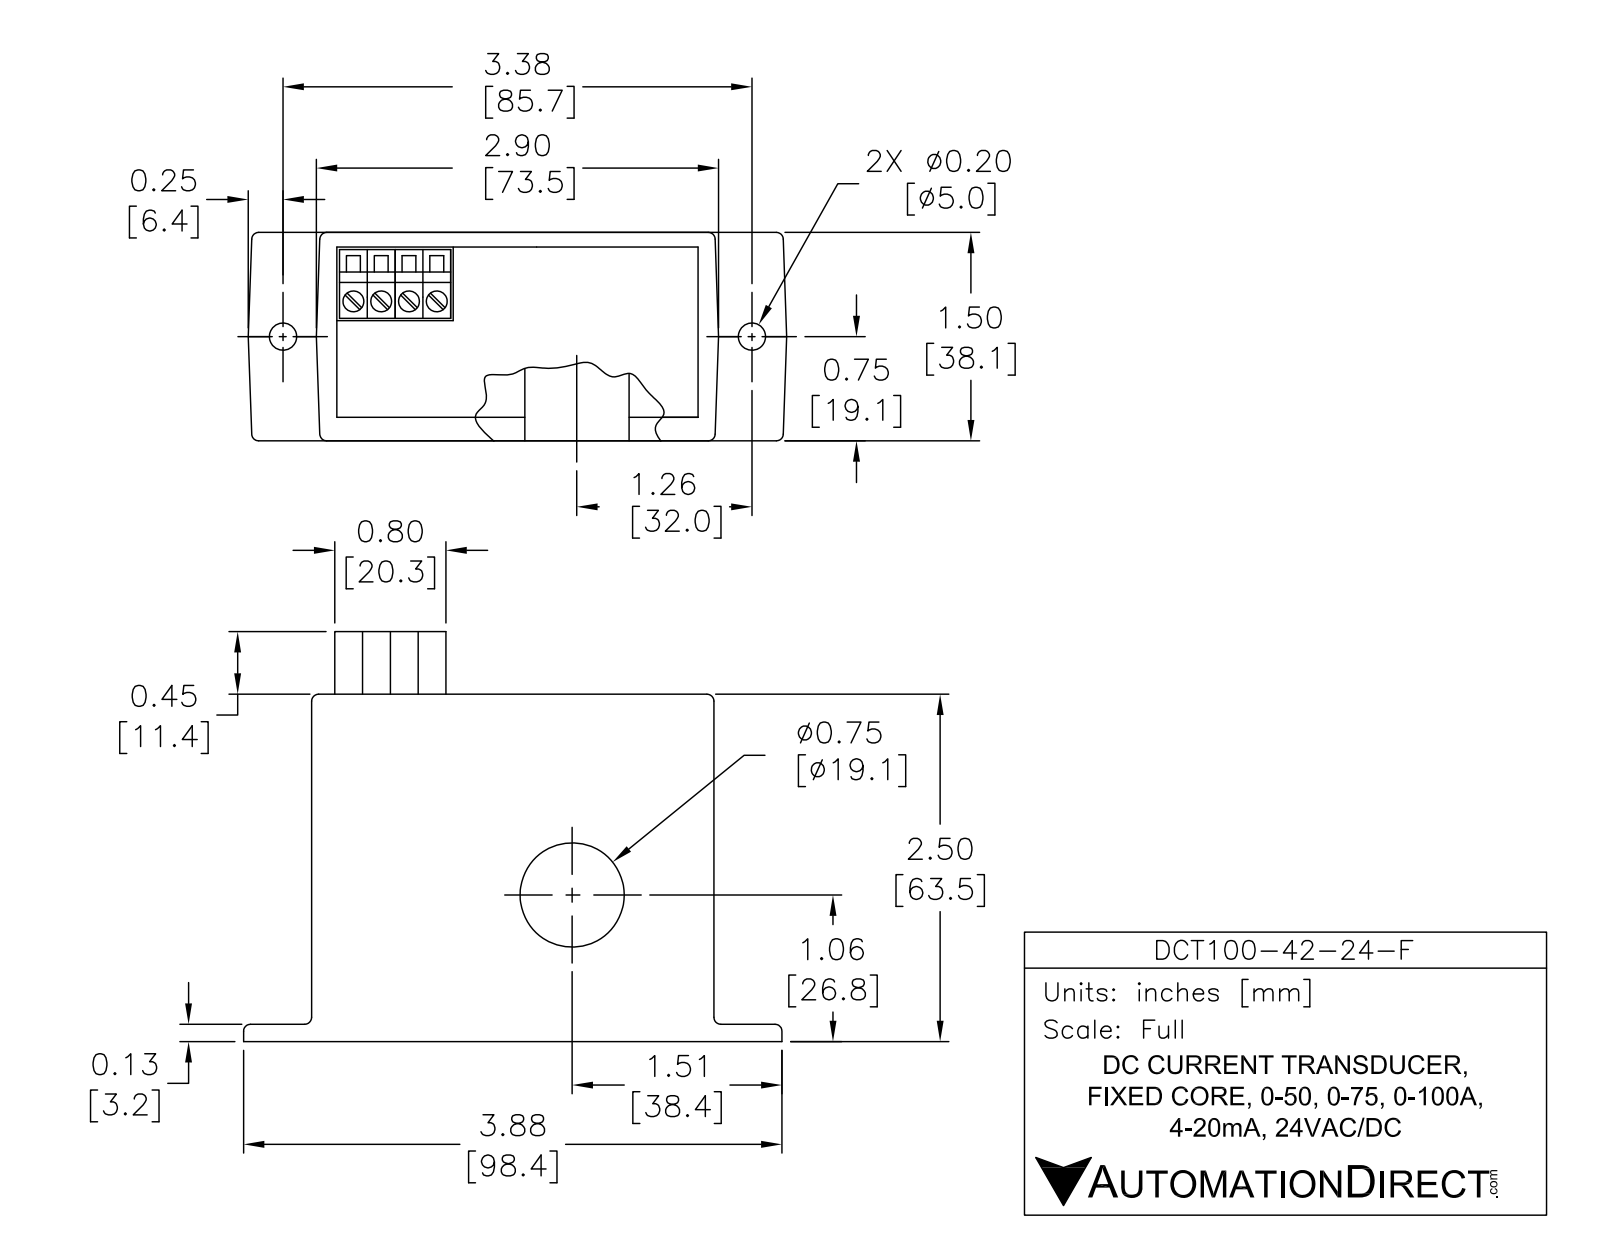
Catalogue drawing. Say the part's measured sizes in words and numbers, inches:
The part is named "DCT100-42-24-F". Its 3-D file was written by "SolidWorks 2017 (AUTOMOTIVE_DESIGN)". It is 3 solids with 131 faces: 85 planar, 38 cylindrical and 8 other. Overall it measures 3.875 by 2.949 by 1.5 inches. Its volume is 10.26 cubic inches and its surface area 39.31 square inches. Round holes: 4 of diameter 0.157, 2 of diameter 0.188, 1 of diameter 0.75. Partial cylindrical surfaces (rounded edges, fillets, slot ends): 22 of radius 0.03. The main face-to-face distances are 1.5, 2.897, 2.45, 2.5, 0.05, 0.125, 2.325, 2.375, 0.125, 2.325. The hole center spacings are 0.197, 0.398, 0.201, 0.596, 0.596, 0.779, 0.971, 1.162.
